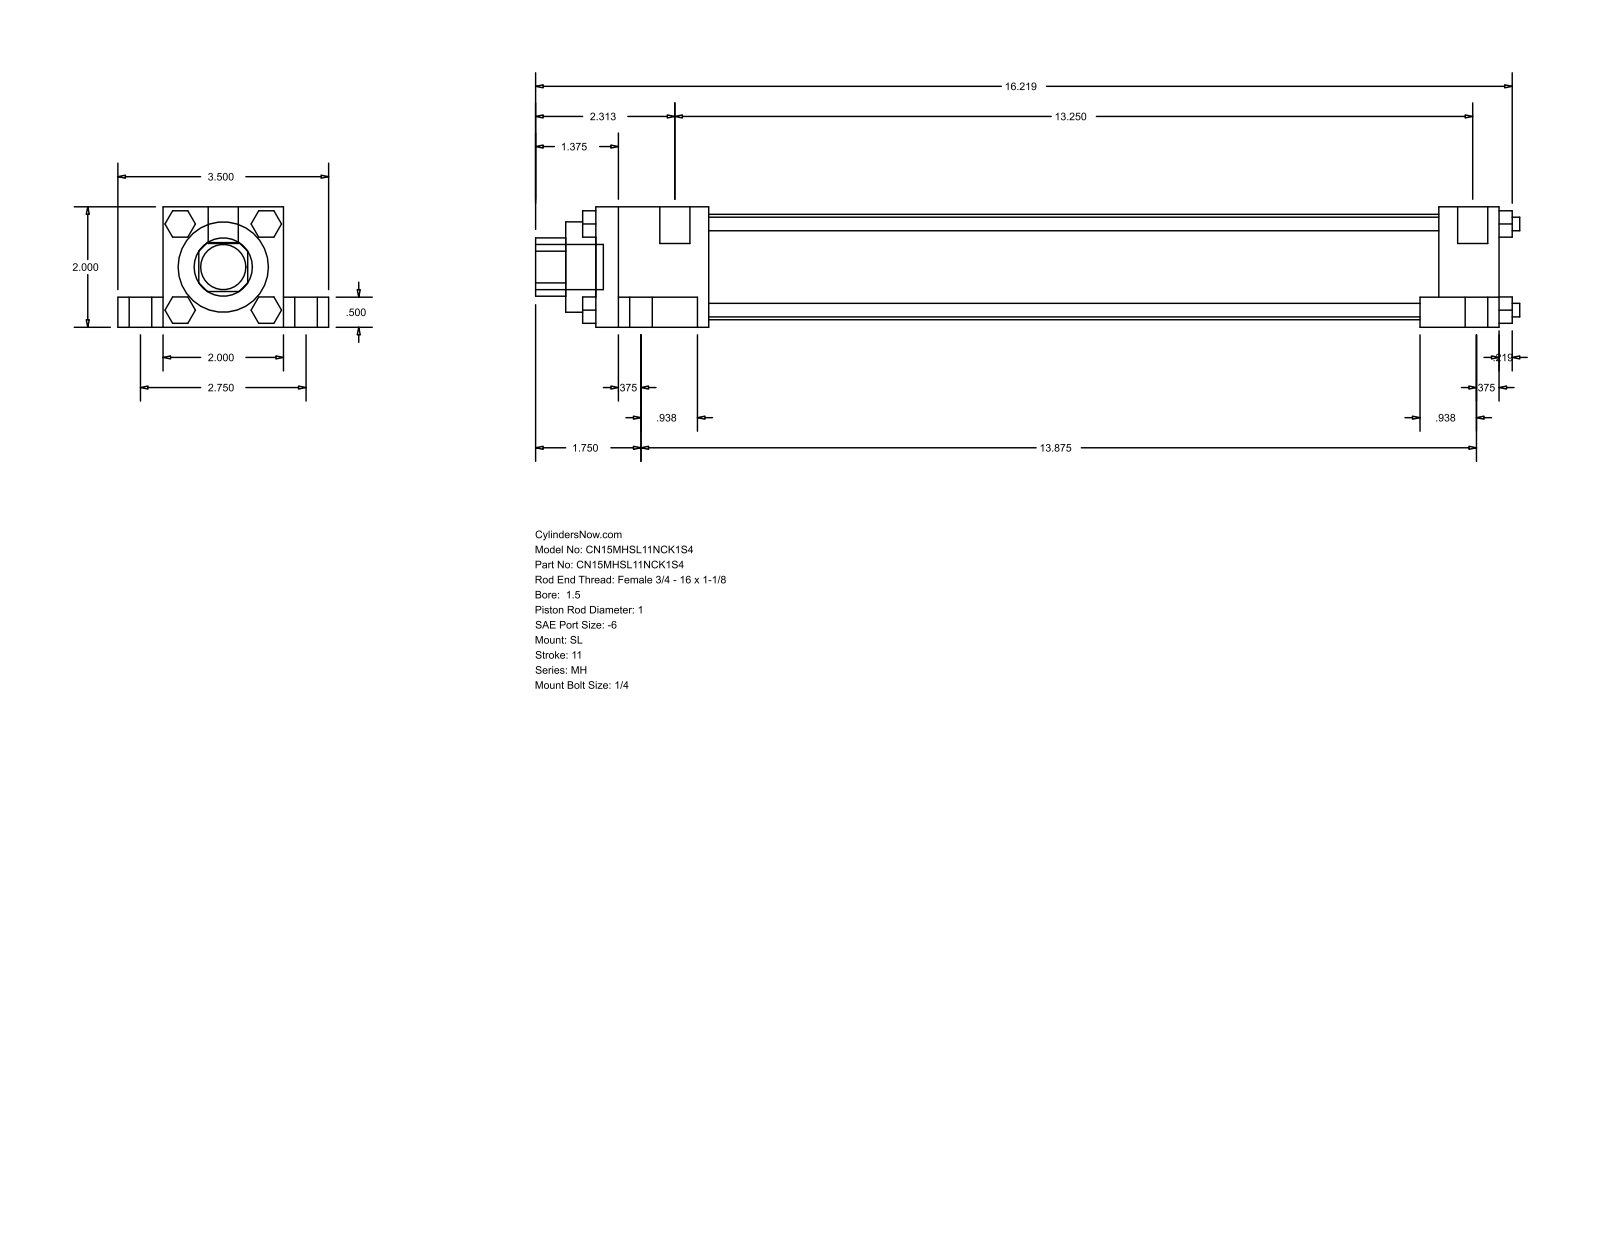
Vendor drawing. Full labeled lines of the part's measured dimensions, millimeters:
Part name (STEP PRODUCT): MH_SL__0150_1
STEP written by: GSSL Pune (CONFIG_CONTROL_DESIGN)
Units: millimetres
Bodies: 0 solids, 148 faces (112 planar, 36 cylindrical, 0 other)
Overall size (bounding box): 415.13 × 88.9 × 50.8
Round holes (diameter × count): ⌀25.4 ×1, ⌀38.1 ×1, ⌀44.45 ×1
Round bosses / shafts (diameter × count): ⌀15.88 ×4, ⌀9.53 ×4, ⌀5.71 ×4, ⌀5.56 ×4, ⌀12.7 ×2, ⌀19.05 ×1
Partial cylindrical surfaces — rounded edges, fillets, slot ends (radius × count): R12.29 ×1
Main face-to-face distances: 50.8, 12.7, 38.1, 19.05, 69.85, 381, 25.4, 9.52, 33.34, 338.14
